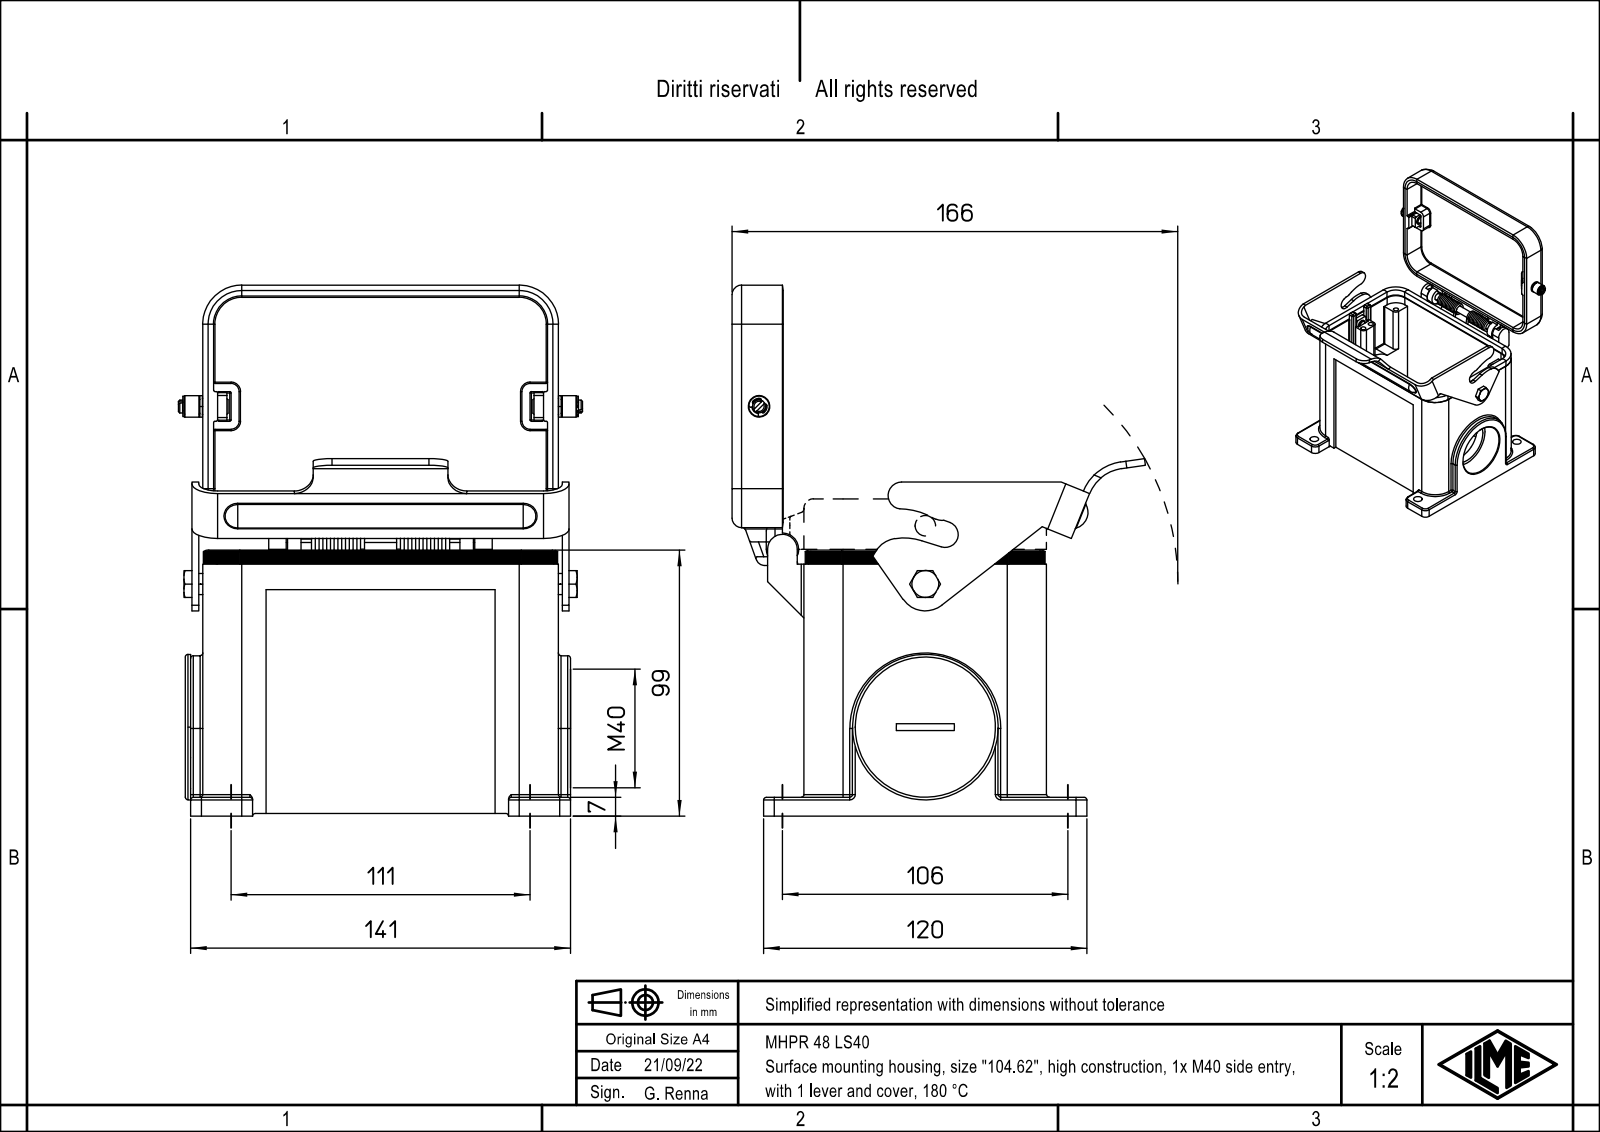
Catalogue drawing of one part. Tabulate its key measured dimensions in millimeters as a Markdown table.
| quantity | value |
| --- | --- |
| part name | MHPR 48 LS40 |
| STEP written by | Autodesk Inventor 7 (AUTOMOTIVE_DESIGN) |
| units | millimeters |
| bodies | 8 solids, 813 faces (202 planar, 291 cylindrical, 320 other) |
| overall size | 199 × 166.2 × 153.5 |
| volume | 477 748 mm³ |
| surface area | 177 851 mm² |
| round holes (diameter × count) | 2.46 × 4, 3.1 × 4, 6.5 × 2, 5.95 × 1, 6 × 1, 8 × 1, 33 × 1, 37 × 1, 40 × 1 |
| round bosses / shafts (diameter × count) | 45 × 1, 8 × 1, 7.8 × 1, 6.2 × 1, 6 × 1, 5 × 1, 4.5 × 1, 3.5 × 1 |
| partial cylindrical surfaces (radius × count) | 1 × 37, 0.38 × 14, 0.5 × 13, 11 × 8, 16 × 8, 3 × 6, 2.5 × 5, 4 × 5 |
| main face-to-face distances | 5, 86, 114, 28, 91, 81, 119, 23, 33, 109 |
| hole center spacings | 27, 104, 107.45, 22.28, 49.12, 54, 57.11, 84.07 |
